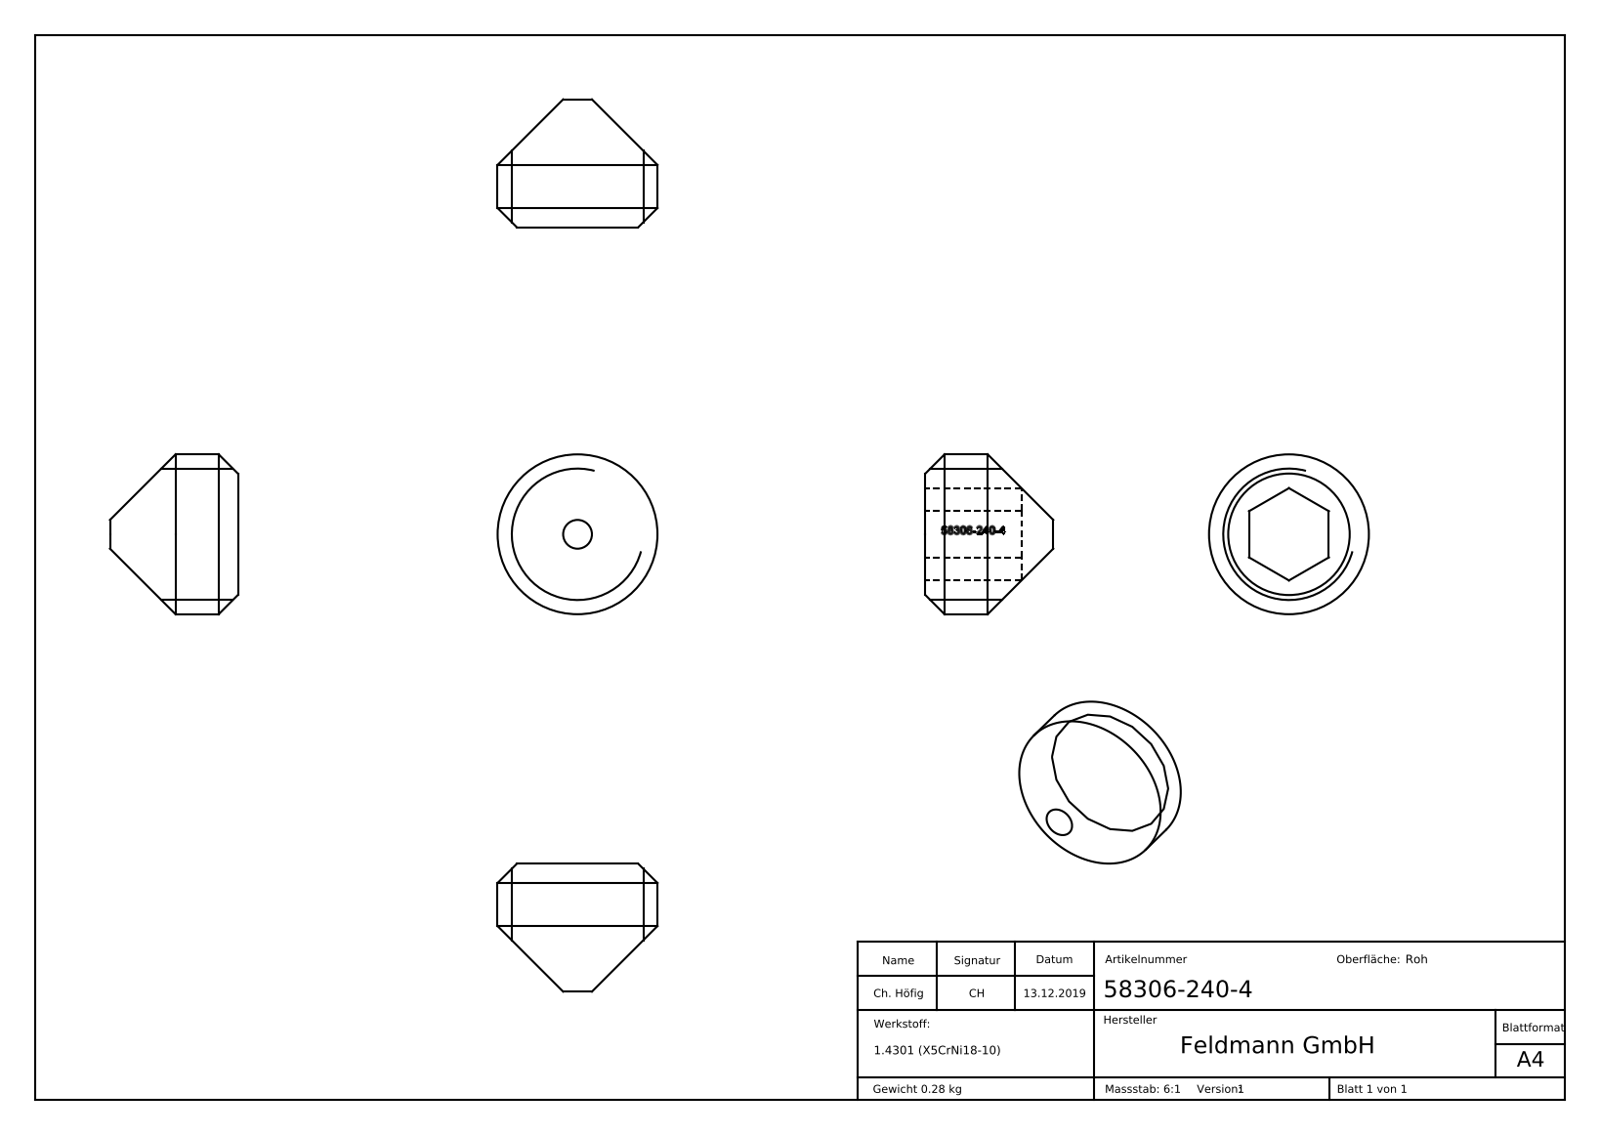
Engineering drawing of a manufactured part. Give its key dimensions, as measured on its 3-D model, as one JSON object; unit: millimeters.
{"part_name": "58306-240-4", "step_written_by": "SolidWorks 2015 (CONFIG_CONTROL_DESIGN)", "units": "millimeters", "bodies": {"solids": 1, "faces": 164, "planar": 78, "cylindrical": 1, "other": 85}, "overall_size": [70, 5, 5], "volume_mm3": 36, "surface_area_mm2": 99, "round_bosses_or_shafts": [[5, 1]], "face_to_face_distances": [2.5, 3, 1, 4, 2.6, 0.52, 0.41, 1.54, 2.06, 0.54]}
